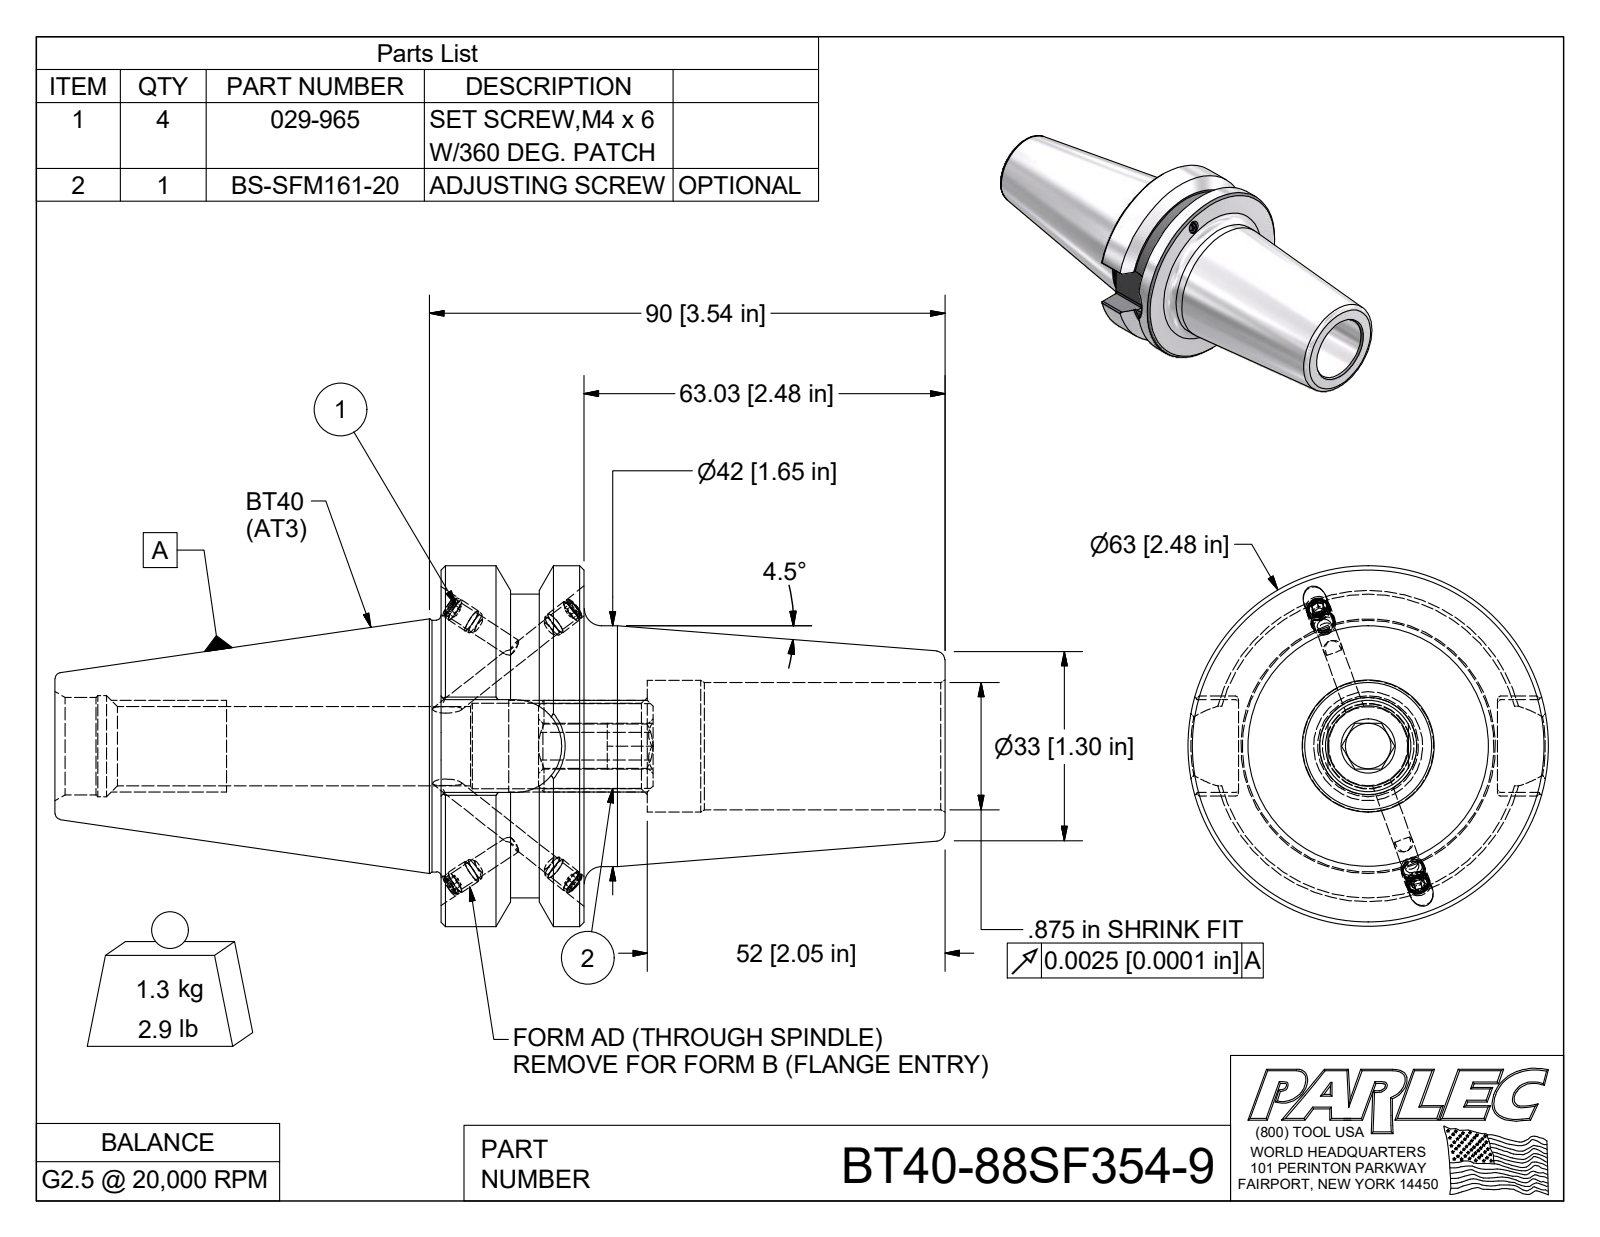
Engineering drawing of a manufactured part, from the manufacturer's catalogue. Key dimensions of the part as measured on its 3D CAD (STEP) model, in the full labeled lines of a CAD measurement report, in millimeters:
Part name (STEP PRODUCT): BT40-88SF354-9; BT40BC-88SF354-9-1; 029-965; BS-SFM161-20
STEP written by: Autodesk Inventor 2009 (AUTOMOTIVE_DESIGN)
Units: millimetres
Bodies: 6 solids, 173 faces (79 planar, 43 cylindrical, 51 other)
Overall size (bounding box): 155.4 × 63 × 63
Volume: 170 400 mm³ · Surface area: 36 320 mm²
Round holes (diameter × count): ⌀3.3 ×4, ⌀4.1 ×4, ⌀17.6 ×1, ⌀22.2 ×1, ⌀23 ×1
Round bosses / shafts (diameter × count): ⌀4.2 ×4, ⌀4 ×4, ⌀63 ×1, ⌀53 ×1, ⌀44.5 ×1, ⌀43.9 ×1, ⌀42 ×1
Partial cylindrical surfaces — rounded edges, fillets, slot ends (radius × count): R0.5 ×8, R8 ×1, R8.1 ×1
Main face-to-face distances: 25, 15.6, 29.6, 88, 63, 45.2, 36, 11, 52, 67.4
